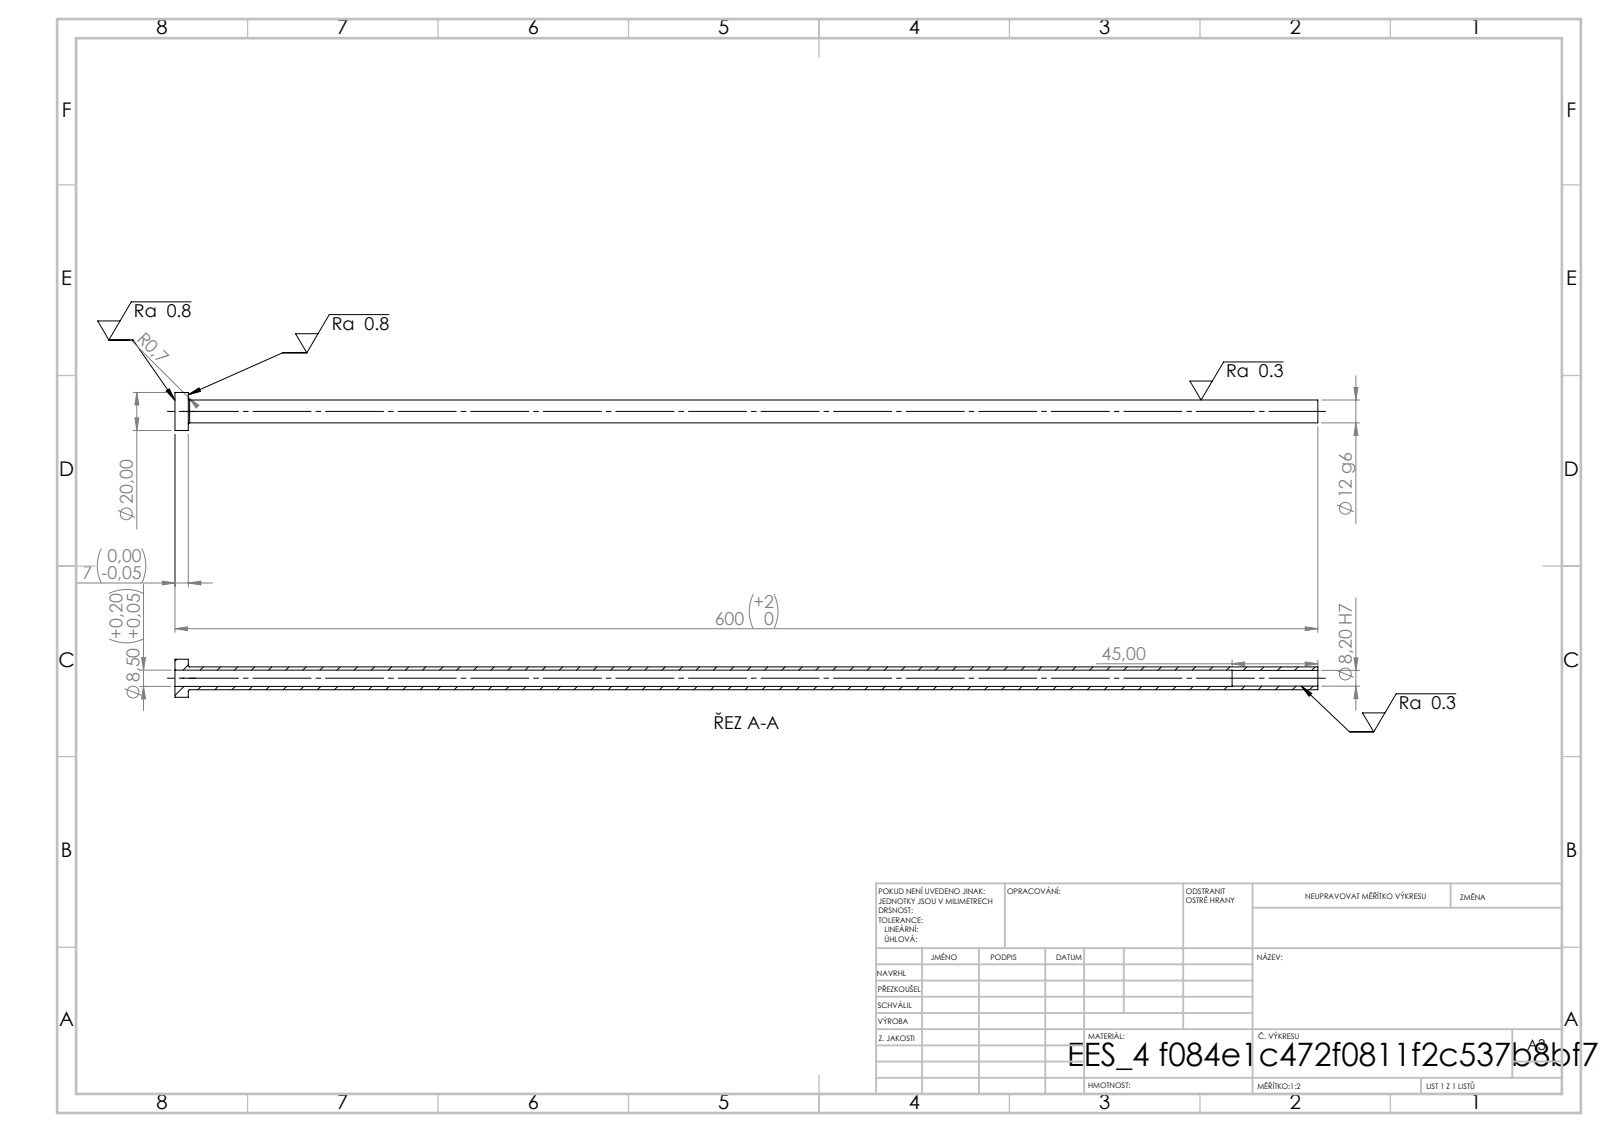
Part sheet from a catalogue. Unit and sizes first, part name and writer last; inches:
Units: inches
Overall size (bounding box): 23.622 × 0.787 × 0.787
Round holes (diameter × count): ⌀0.323 ×1, ⌀0.335 ×1
Round bosses / shafts (diameter × count): ⌀0.787 ×1, ⌀0.472 ×1
Main face-to-face distances: 0.276, 23.622, 23.346, 21.85, 21.575, 1.772
Volume: 2.16 in³ · Surface area: 60.89 in²
Bodies: 1 solid, 14 faces (4 planar, 8 cylindrical, 2 other)
STEP written by: SolidWorks 2019 (CONFIG_CONTROL_DESIGN)
